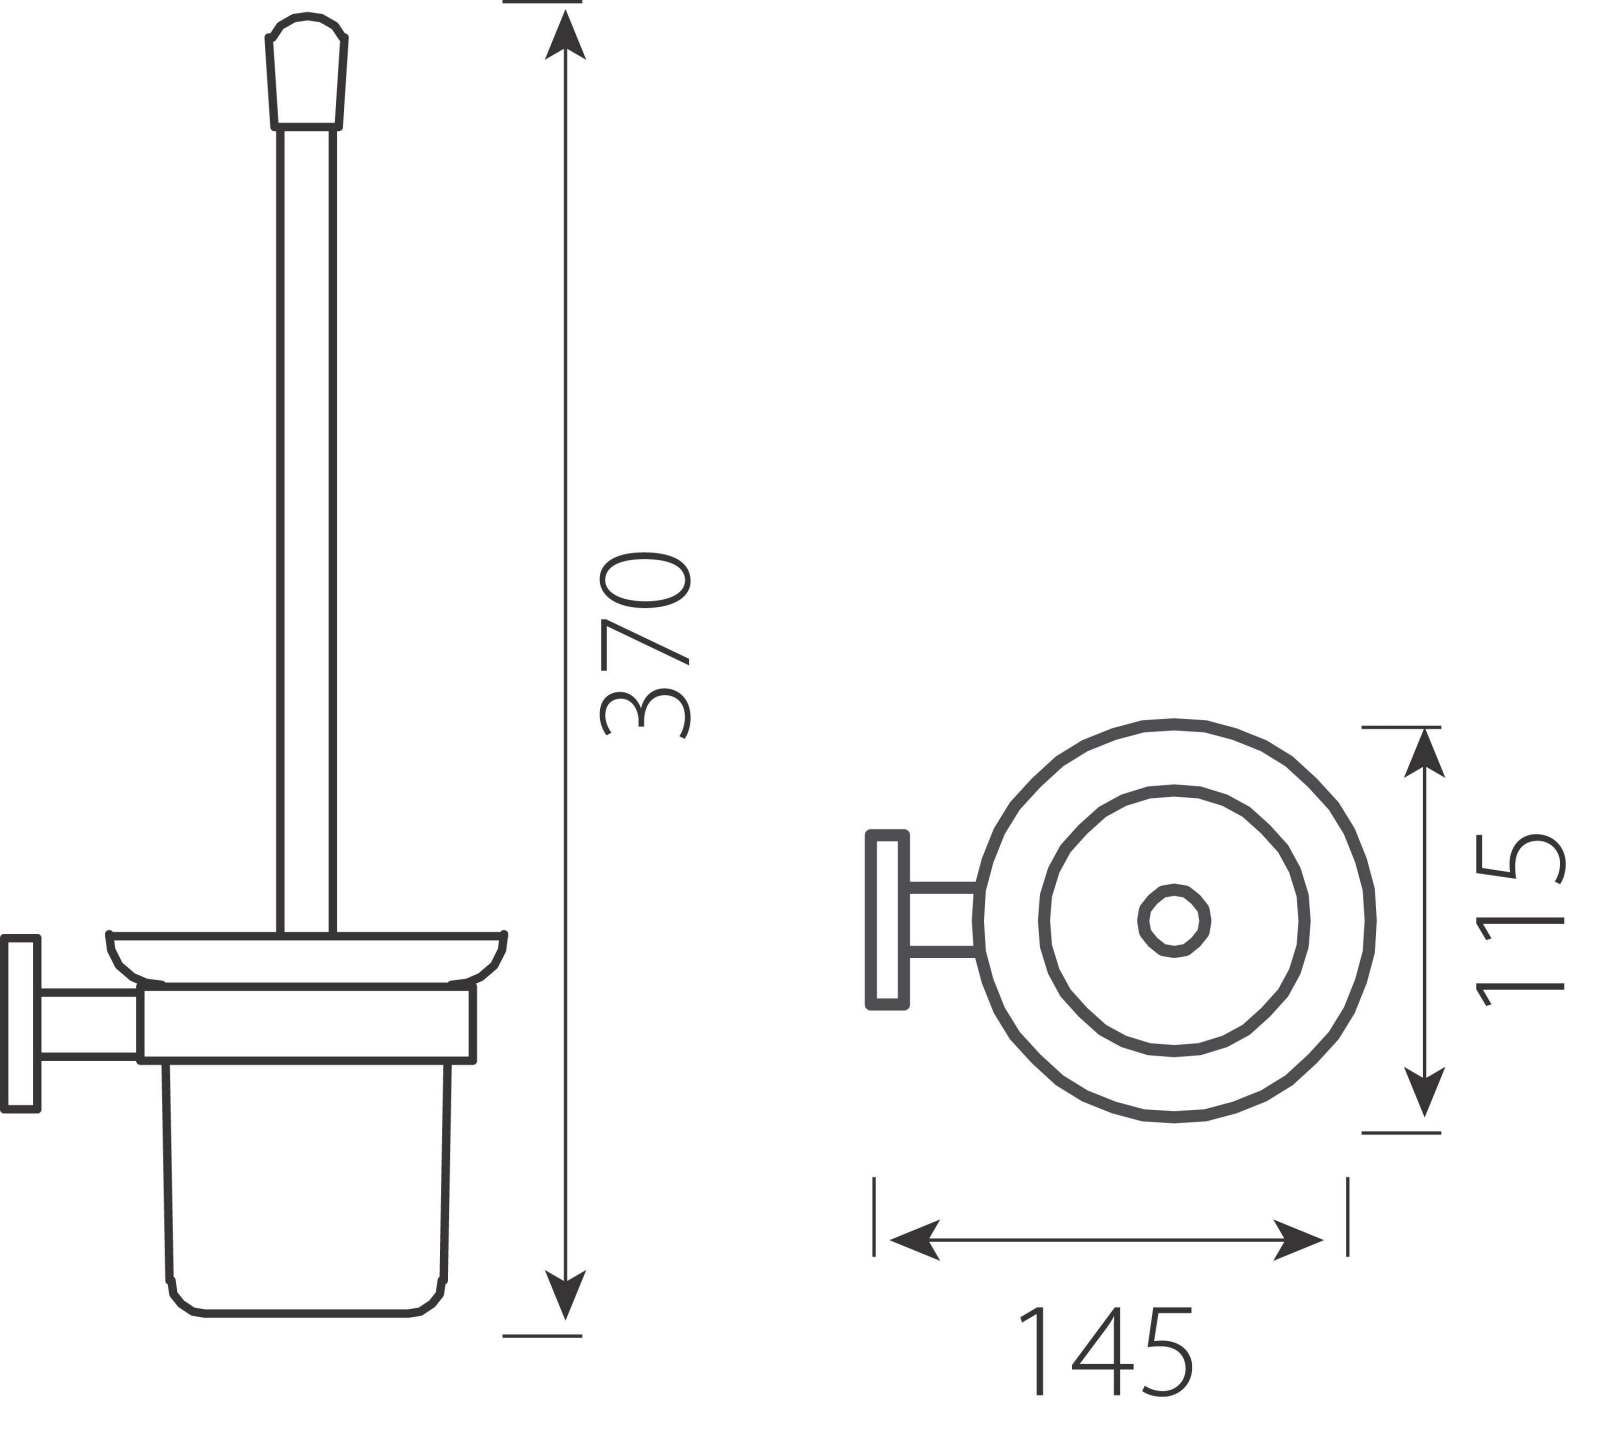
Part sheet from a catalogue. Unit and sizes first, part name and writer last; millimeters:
Units: millimetres
Overall size (bounding box): 370.42 × 143.52 × 114.98
Round holes (diameter × count): ⌀4 ×1, ⌀4.2 ×1, ⌀5 ×1, ⌀6 ×1, ⌀6.8 ×1, ⌀7.8 ×1, ⌀9.6 ×1, ⌀14.3 ×1, ⌀17.8 ×1, ⌀20 ×1, ⌀87 ×1, ⌀89 ×1
Round bosses / shafts (diameter × count): ⌀4 ×84, ⌀94 ×1, ⌀93 ×1, ⌀52 ×1, ⌀27.7 ×1, ⌀25 ×1, ⌀19 ×1, ⌀18 ×1
Partial cylindrical surfaces — rounded edges, fillets, slot ends (radius × count): R2 ×10, R0.2 ×8, R0.1 ×6, R2.6 ×4, R5.1 ×1, R37 ×1
Main face-to-face distances: 1, 1.8, 21, 20, 7, 1.2, 10, 8.2, 22, 2
Hole centre spacings: 82.53
Volume: 200 743 mm³ · Surface area: 170 770 mm²
Bodies: 15 solids, 753 faces (157 planar, 412 cylindrical, 184 other)
Part name (STEP PRODUCT): 11马杯圈塑料; 1288; 11马桶杯圈; 马桶刷（74） (+1 more)
STEP written by: SolidWorks 2018 (CONFIG_CONTROL_DESIGN)
